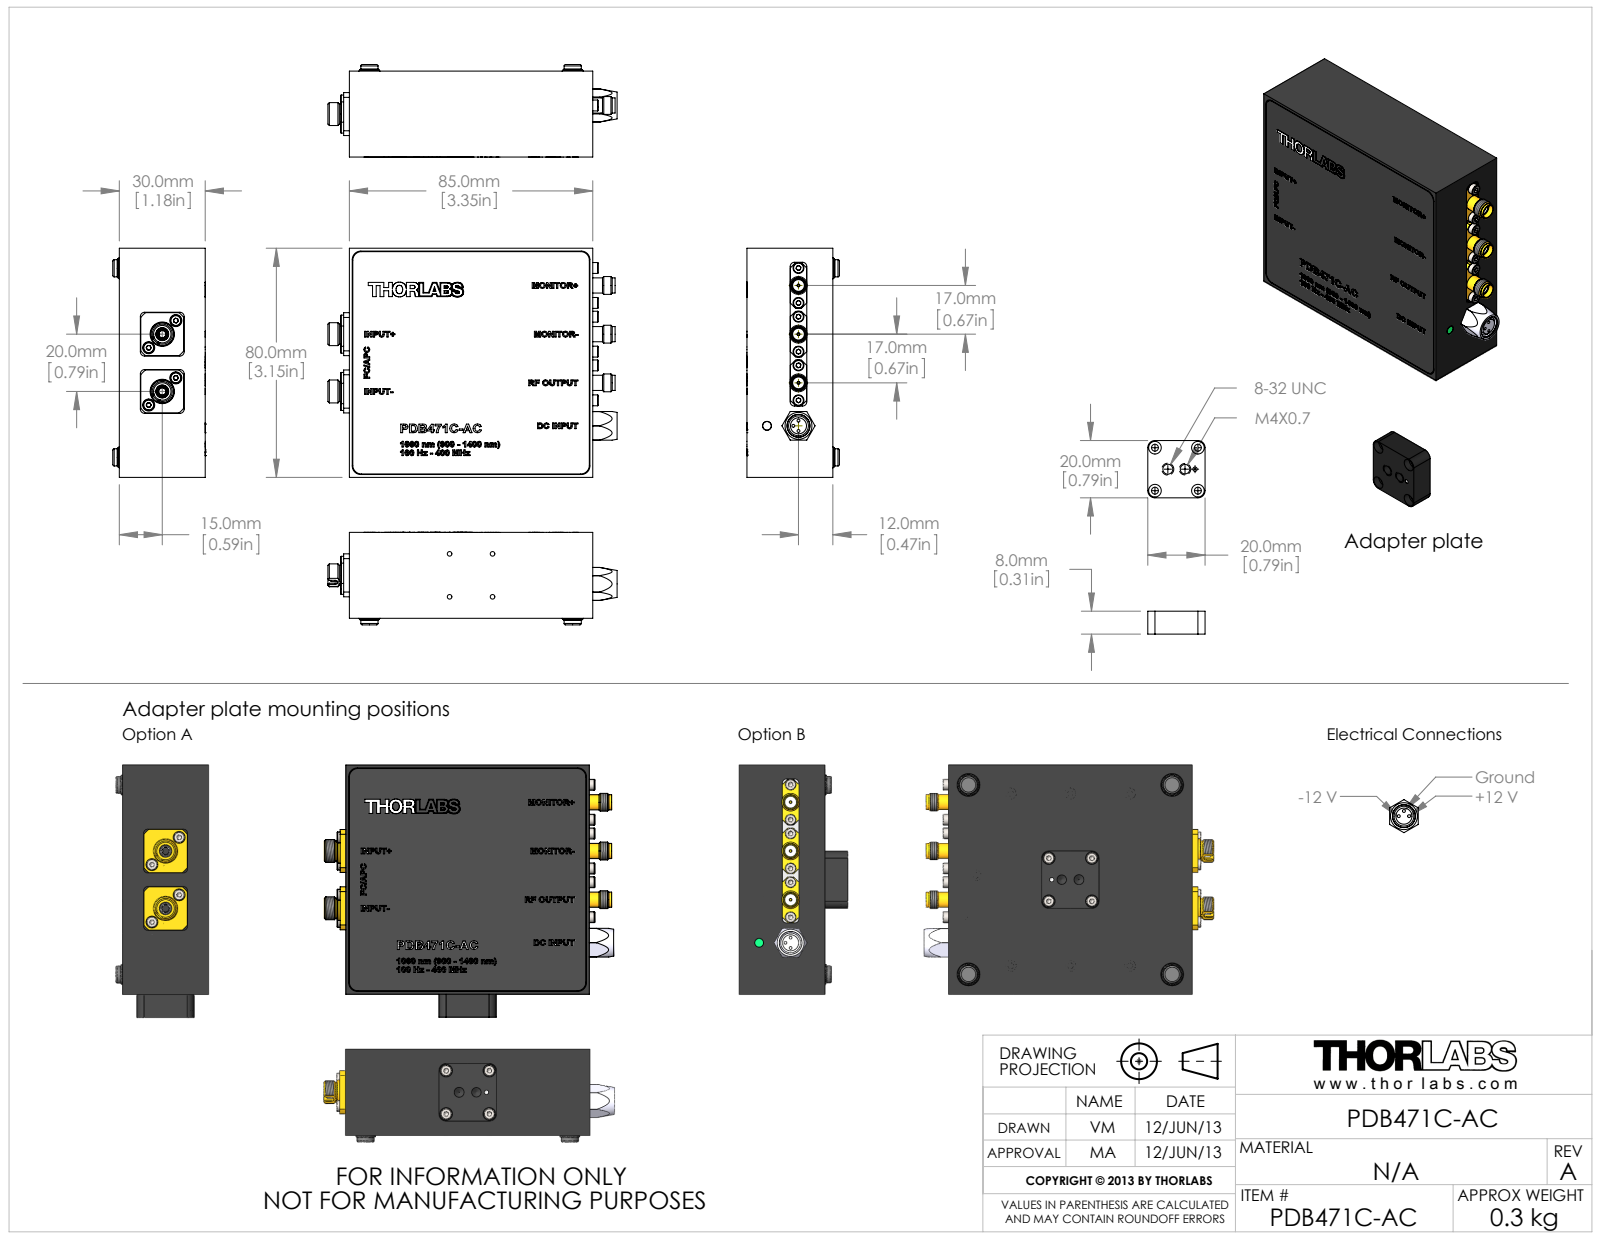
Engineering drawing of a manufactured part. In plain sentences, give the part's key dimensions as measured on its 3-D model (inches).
The part is named "M0075-22-0001 PDA10Bx (RKMF); M0092-0699 Grundkörper PDB480C-AC Rev C; PDB480C-AC Rev C; M0091-90-0003 PDA10Bx (Gerätefüsse) (+8 more)". Its 3-D file was written by "SolidWorks 2012 (AUTOMOTIVE_DESIGN)". It is 84 solids with 3153 faces: 1818 planar, 542 cylindrical and 793 other. Overall it measures 3.976 by 3.465 by 1.496 inches. Its volume is 5.438 cubic inches and its surface area 90.06 square inches. Round holes: 29 of diameter 0.063, 8 of diameter 0.094, 8 of diameter 0.173, 7 of diameter 0.315, 6 of diameter 0.102, 4 of diameter 0.059, 3 of diameter 0.031, 3 of diameter 0.039, 3 of diameter 0.161, 3 of diameter 0.165, 3 of diameter 0.185, 2 of diameter 0.126. Round bosses or shafts: 25 of diameter 0.15, 25 of diameter 0.079, 8 of diameter 0.165, 8 of diameter 0.091, 6 of diameter 0.236, 4 of diameter 0.062, 3 of diameter 0.245, 3 of diameter 0.209. Partial cylindrical surfaces (rounded edges, fillets, slot ends): 12 of radius 0.059, 12 of radius 0.118, 10 of radius 0.197, 8 of radius 0.098, 4 of radius 0.04, 3 of radius 0.315, 2 of radius 0.374, 1 of radius 0.226. The main face-to-face distances are 1.181, 1.169, 0.236, 0.933, 0.945, 0.217, 3.15, 3.346, 0.079, 2.933. The hole center spacings are 0.591, 0.344, 0.508, 0.24, 0.669, 0.111, 0.298, 0.429.
